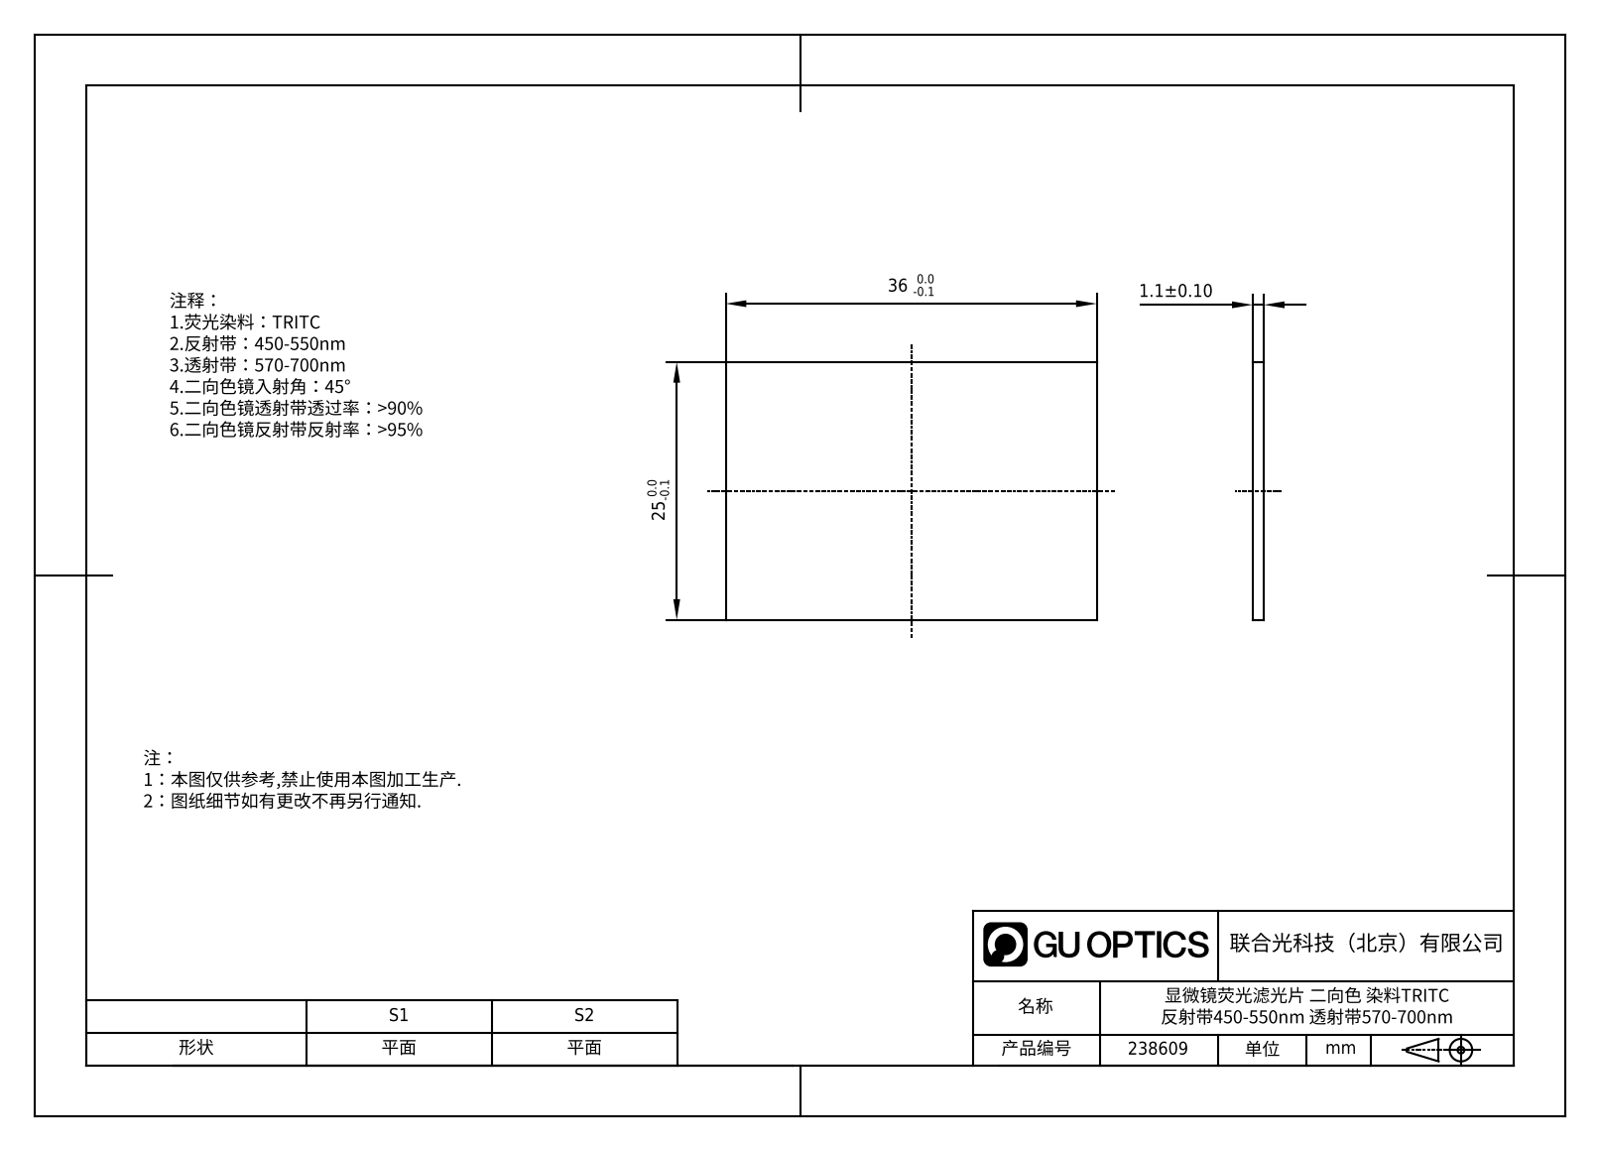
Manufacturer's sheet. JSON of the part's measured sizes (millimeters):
{"part_name": "GDMLPH-560-25x36", "step_written_by": "SolidWorks 2022 (AUTOMOTIVE_DESIGN)", "units": "millimeters", "bodies": {"solids": 1, "faces": 6, "planar": 6, "cylindrical": 0, "other": 0}, "overall_size": [36, 25, 1.1], "volume_mm3": 990, "surface_area_mm2": 1934, "face_to_face_distances": [1.1, 25, 36]}
